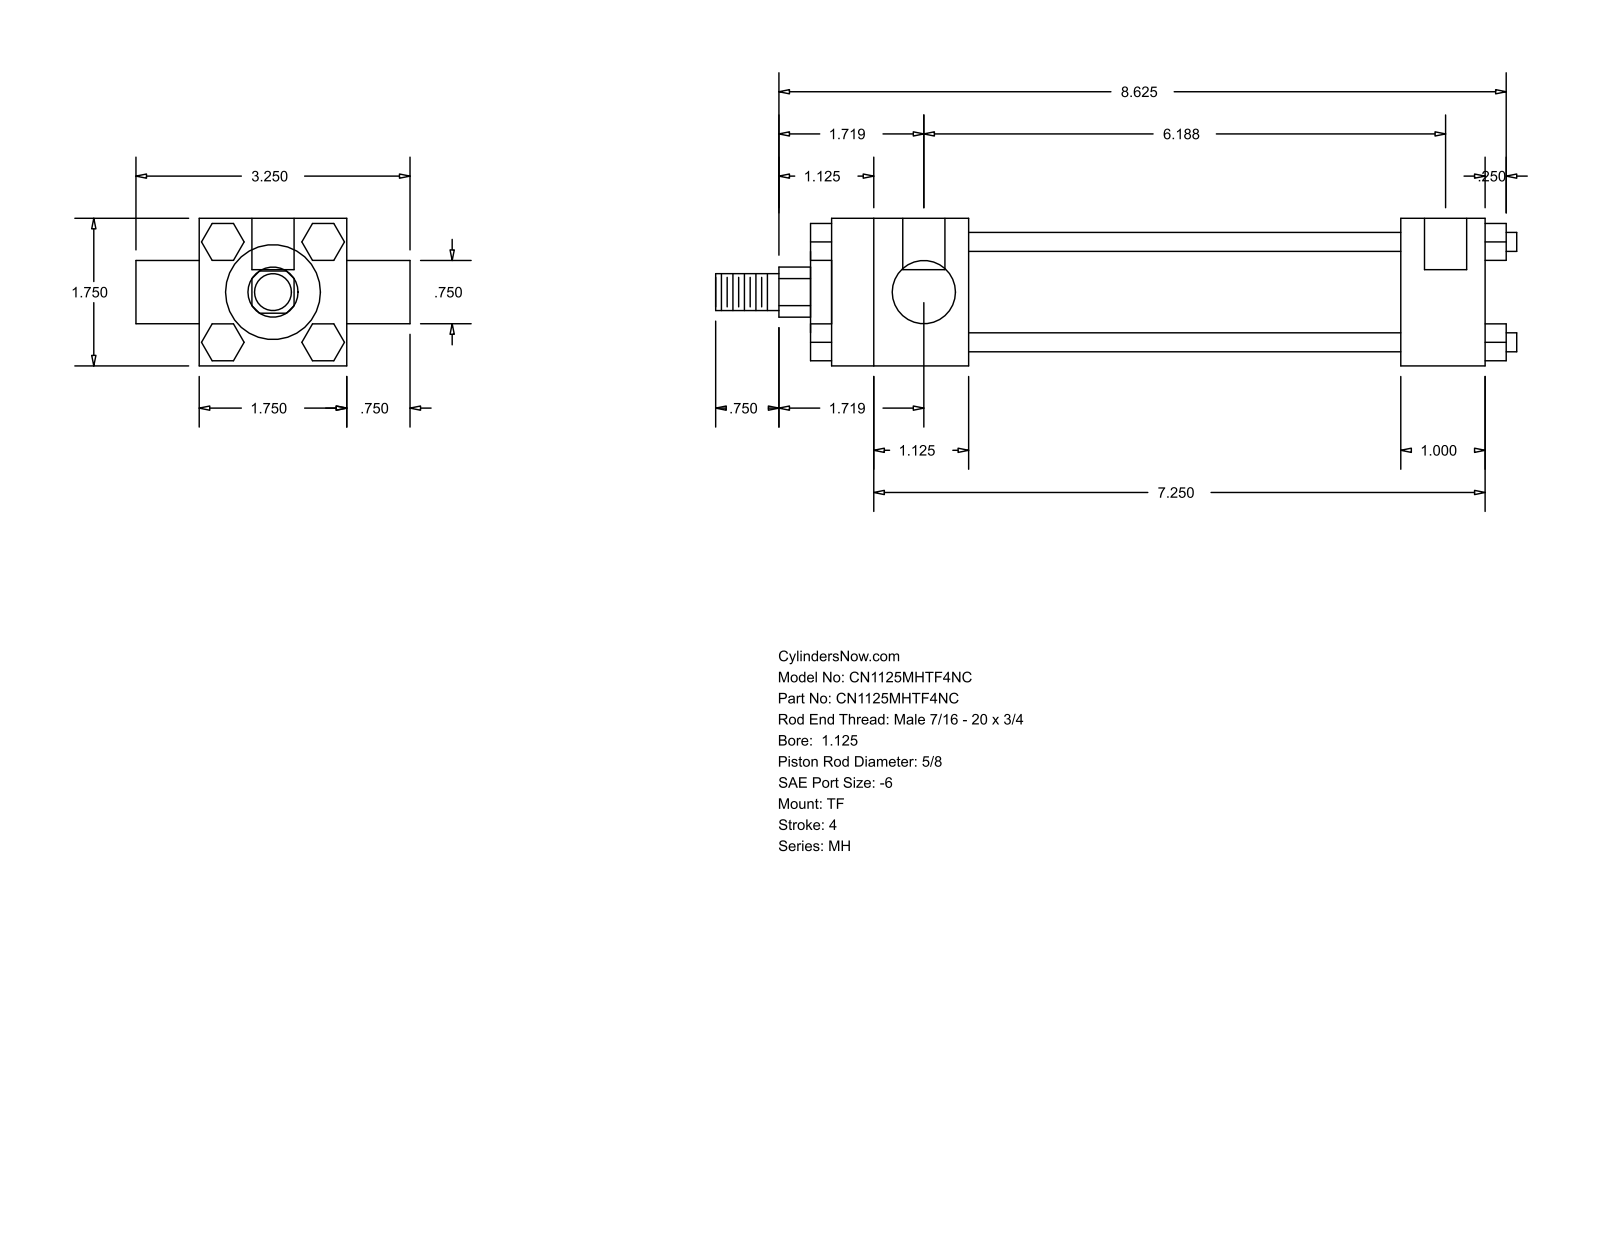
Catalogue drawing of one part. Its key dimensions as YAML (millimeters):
part_name: "MH_TF__0112_0.625"
step_written_by: "GSSL Pune (CONFIG_CONTROL_DESIGN)"
units: millimeters
bodies: {solids: 0, faces: 120, planar: 92, cylindrical: 28, other: 0}
overall_size: [241.3, 82.55, 44.45]
round_holes:
  - {diameter: 5.56, count: 3}
  - {diameter: 12.7, count: 2}
round_bosses_or_shafts:
  - {diameter: 5.71, count: 4}
  - {diameter: 34.92, count: 1}
  - {diameter: 28.57, count: 1}
  - {diameter: 19.05, count: 1}
  - {diameter: 15.88, count: 1}
  - {diameter: 11.11, count: 1}
partial_cylinders:
  - {radius: 7.54, count: 1}
face_to_face_distances: [44.46, 6.35, 203.19, 11.11, 25.4, 130.17, 155.57, 41.27, 171.44, 196.84]
hole_center_spacings: [3.17, 153.99, 157.16]
